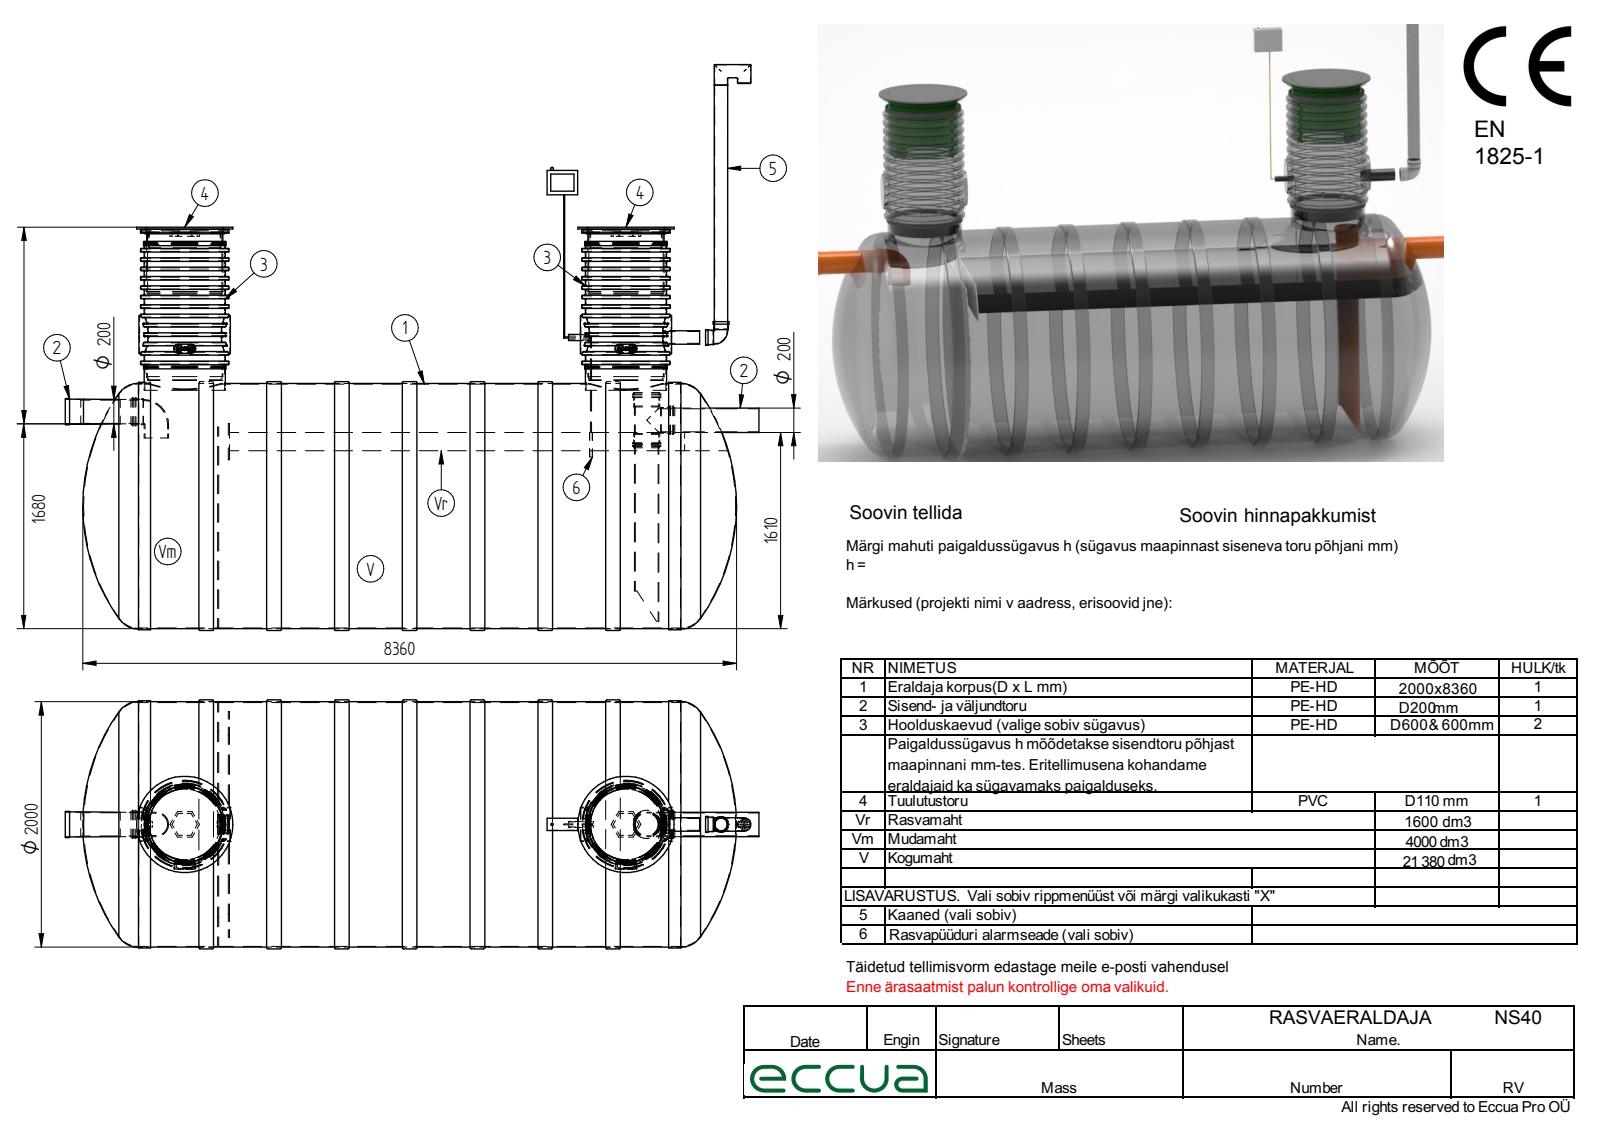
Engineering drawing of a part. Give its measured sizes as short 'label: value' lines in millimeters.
name: Rasvaeraldaja NS40; Rasvaeraldaja NS40 ots2 D2000 21.03.23; rasvaeraldaja NS40_silinder 21.03.23; 2000 Ribi (+8 more)
written by: Solid Edge (AUTOMOTIVE_DESIGN)
unit: mm
bodies: 54 solids, 1274 faces (493 planar, 396 cylindrical, 385 other)
size: 8759 × 4155.5 × 2618.53
volume: 4 943 000 000 mm³; area: 285 500 000 mm²
holes: 31× ⌀10, 3× ⌀103.2, 3× ⌀200, 2× ⌀6, 2× ⌀100, 2× ⌀188, 2× ⌀220, 2× ⌀595, 2× ⌀600, 2× ⌀609, 2× ⌀615, 2× ⌀630
bosses: 4× ⌀110, 3× ⌀212, 3× ⌀8.5, 2× ⌀790, 2× ⌀725, 2× ⌀678.5, 2× ⌀665, 2× ⌀650
rounds: 8× R5, 8× R30, 8× R35, 6× R3, 2× R135, 2× R140, 2× R289.9, 1× R130
face distances: 150, 8, 5, 195, 45, 88, 1126, 1874, 1724, 1679
hole spacings: 40, 49.88, 72.08, 34.71, 62.55, 26.75, 78, 17.81
